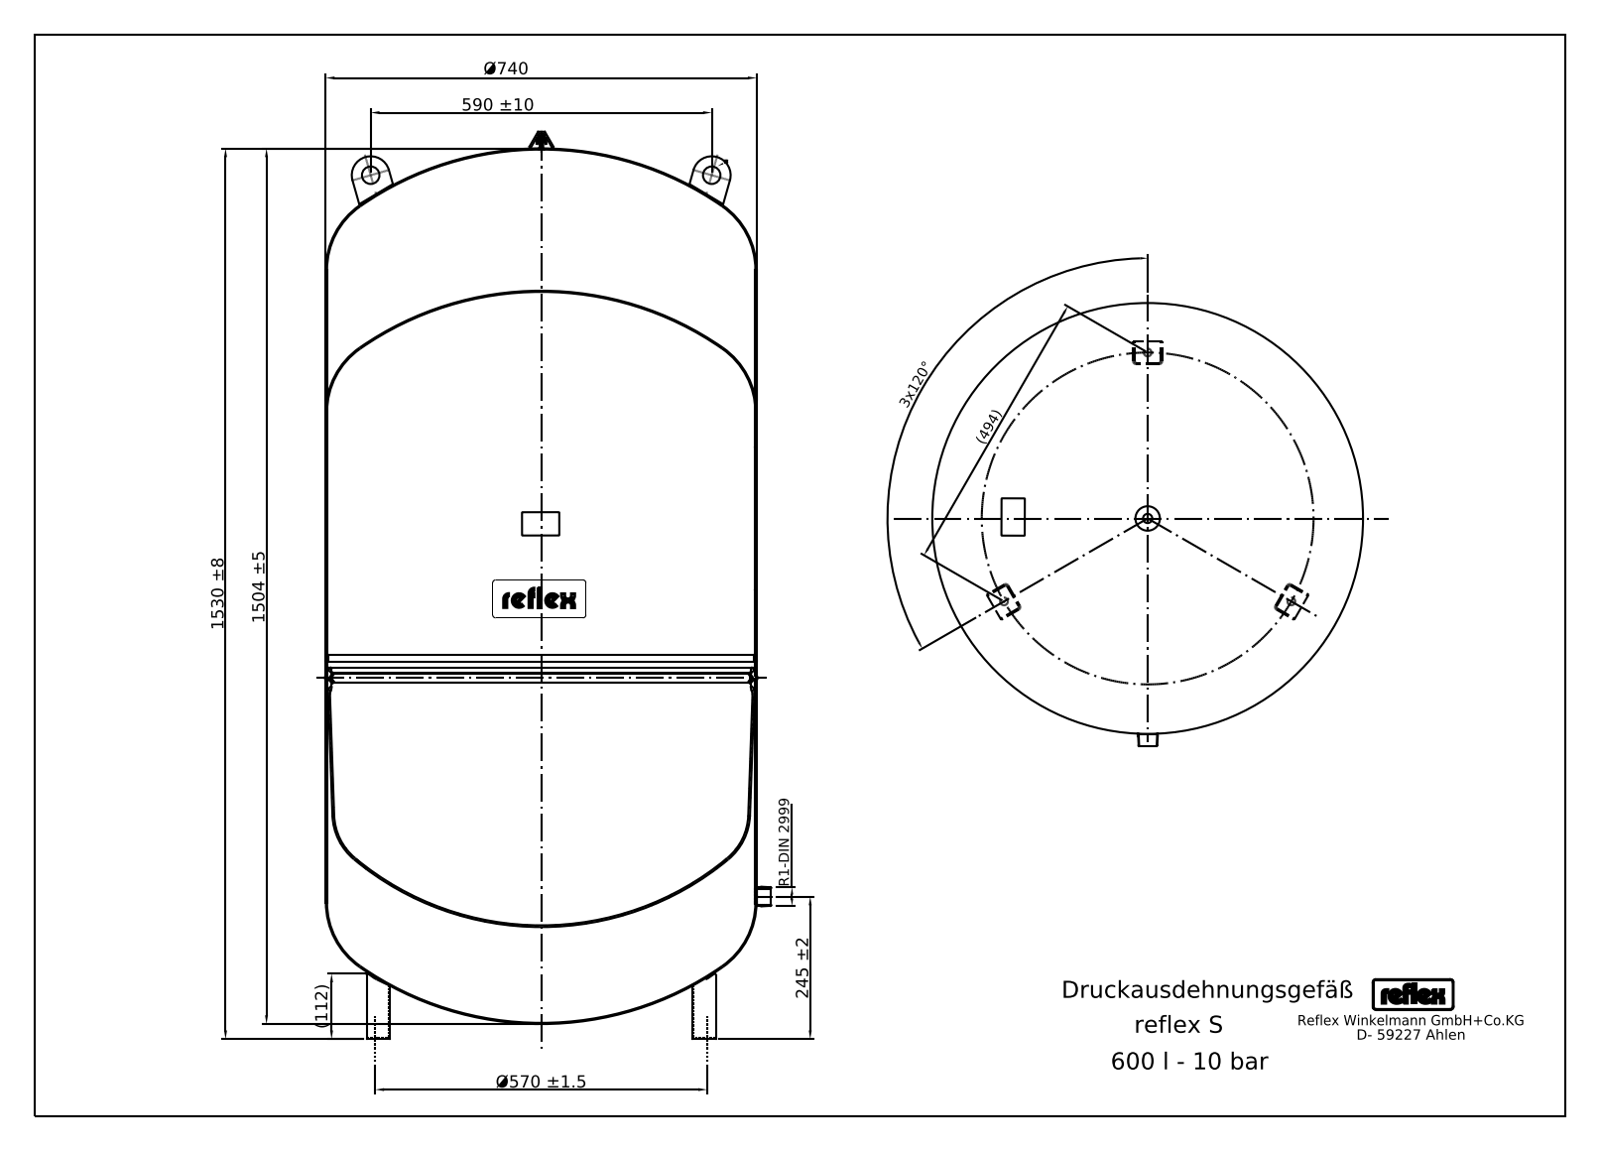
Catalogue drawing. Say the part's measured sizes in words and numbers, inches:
Its 3-D file was written by "Mechanical Desktop 2008 (CONFIG_CONTROL_DESIGN)". It is 16 solids with 248 faces: 100 planar, 91 cylindrical and 57 other. Overall it measures 61.368 by 30.291 by 29.48 inches. Its volume is 36 080 cubic inches and its surface area 8 799 square inches. Round holes: 3 of diameter 0.528, 1 of diameter 0.555. Round bosses or shafts: 1 of diameter 29.134, 1 of diameter 1.327, 1 of diameter 0.673, 1 of diameter 0.354, 1 of diameter 0.236. Partial cylindrical surfaces (rounded edges, fillets, slot ends): 15 of radius 0.039, 15 of radius 0.098, 15 of radius 0.197, 4 of radius 0.155, 3 of radius 0.062, 2 of radius 0.106, 2 of radius 0.186, 2 of radius 0.256. The main face-to-face distances are 44.331, 0.098, 1.87, 1.772, 1.969, 17.323, 27.008, 8.386, 25.709, 52.717. The hole center spacings are 11.22, 19.435.
